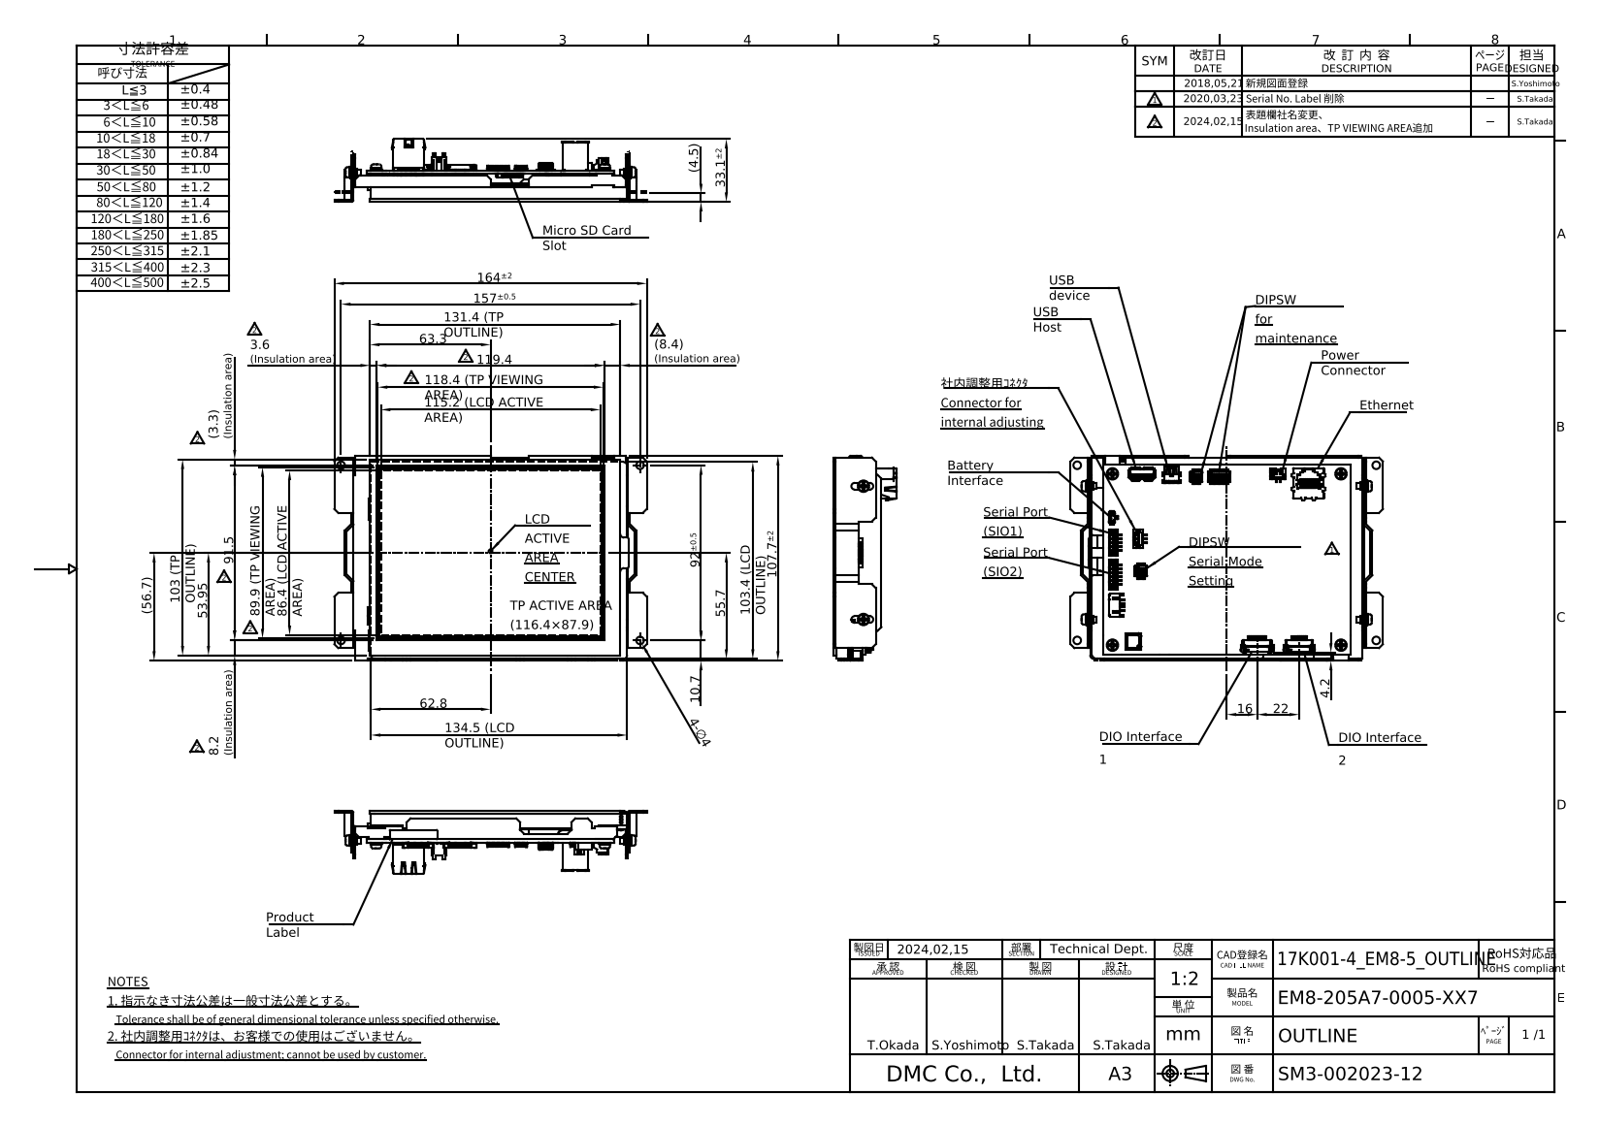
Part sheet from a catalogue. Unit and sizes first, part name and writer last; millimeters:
Units: millimetres
Overall size (bounding box): 164 × 107.71 × 33.06
Round holes (diameter × count): ⌀3.5 ×4, ⌀4 ×4, ⌀8 ×4, ⌀1.2 ×3, ⌀2.46 ×2, ⌀4.52 ×2, ⌀1.33 ×1, ⌀7 ×1
Round bosses / shafts (diameter × count): ⌀6 ×6, ⌀5.5 ×6, ⌀3 ×6, ⌀4 ×4, ⌀3.6 ×4, ⌀1.5 ×3, ⌀4.5 ×2, ⌀0.5 ×1
Partial cylindrical surfaces — rounded edges, fillets, slot ends (radius × count): R0.1 ×268, R0.2 ×95, R0.3 ×66, R0.15 ×60, R0.5 ×38, R0.25 ×28, R0.4 ×18, R0.13 ×16
Main face-to-face distances: 1.6, 1, 13.4, 15, 15.16, 13.56, 1.54, 16.54, 14.94, 1.38
Hole centre spacings: 18.67, 19.04, 89.43, 90, 92, 96.29, 106.31, 120
Volume: 156 085 mm³ · Surface area: 136 356 mm²
Bodies: 1 solid, 8093 faces (6360 planar, 1567 cylindrical, 166 other)
Part name (STEP PRODUCT): HP_EM8-205A7-0005-107
STEP written by: Autodesk Inventor 2020 (AUTOMOTIVE_DESIGN)
